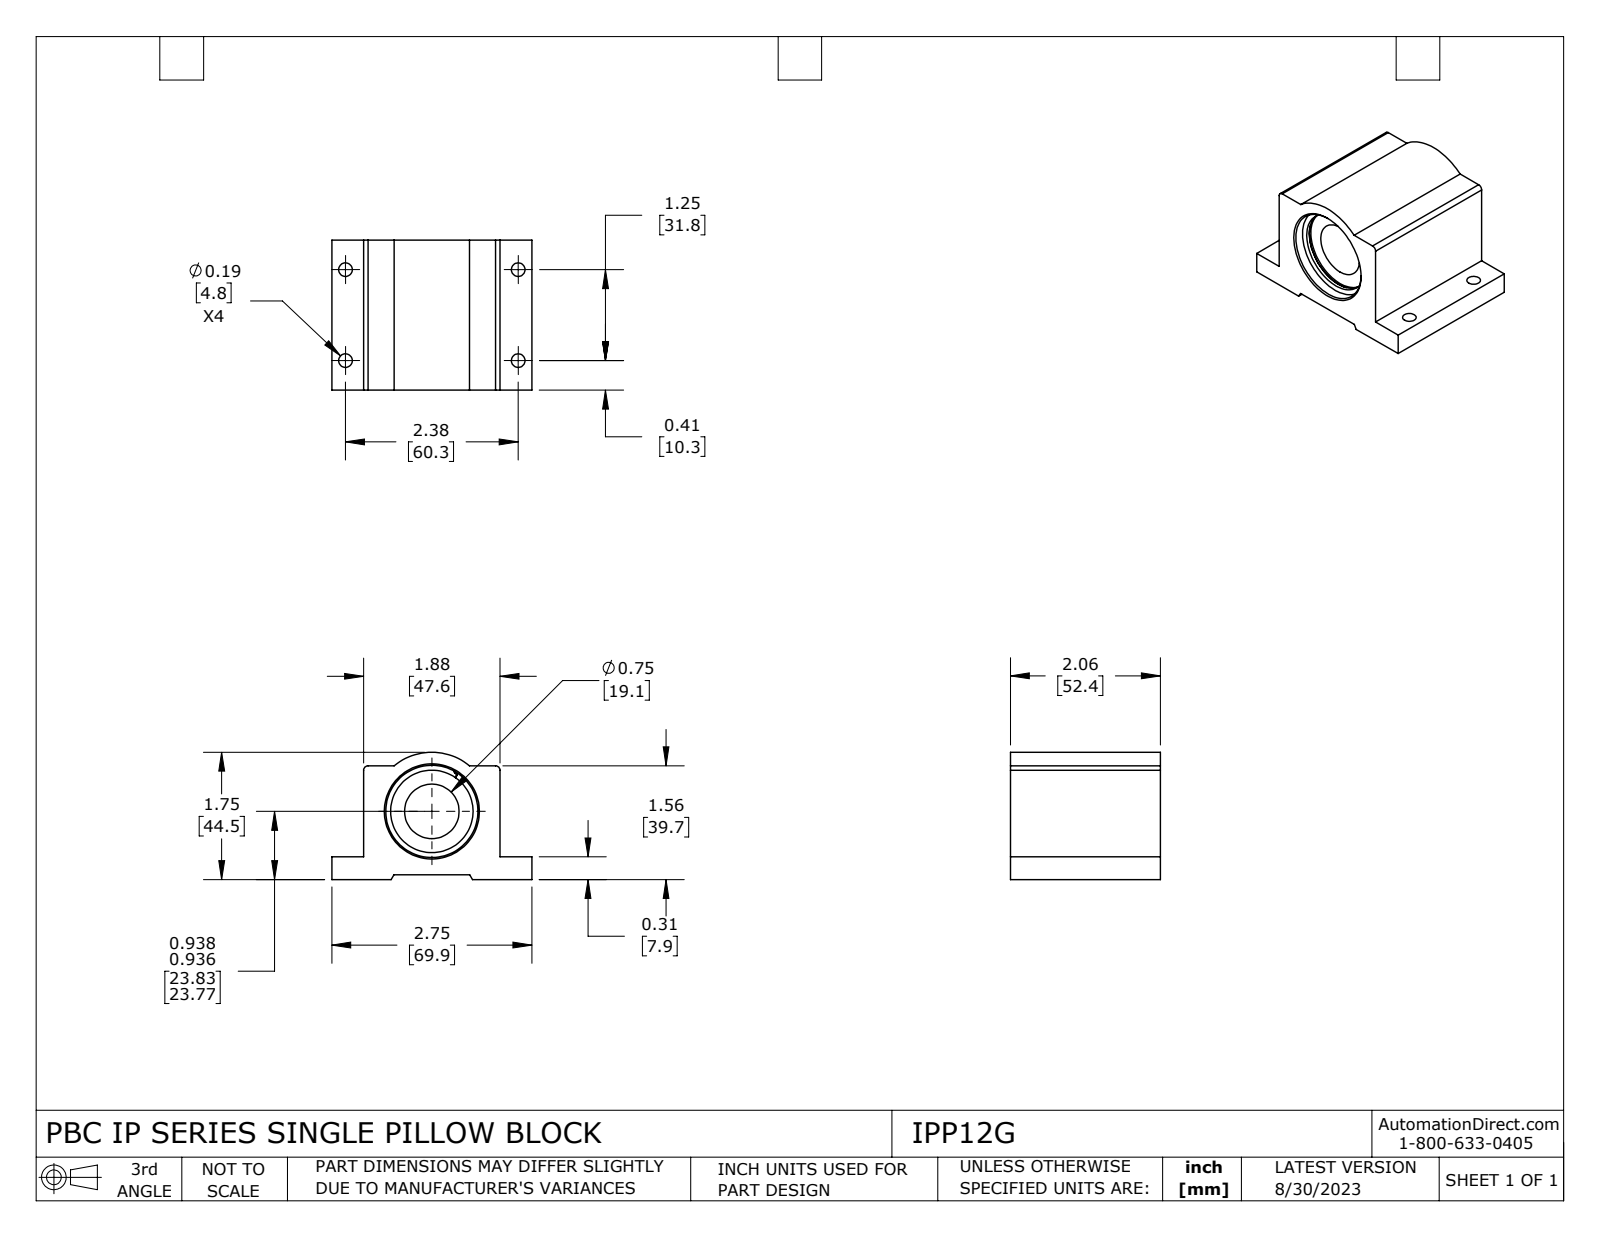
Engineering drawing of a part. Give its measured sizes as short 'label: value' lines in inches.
name: IPP12G
written by: SolidWorks 2021 (CONFIG_CONTROL_DESIGN)
unit: in
bodies: 4 solids, 126 faces (43 planar, 63 cylindrical, 20 other)
size: 2.75 × 2.063 × 1.75
volume: 5.358 in³; area: 45.8 in²
holes: 4× ⌀0.187, 1× ⌀0.75, 1× ⌀1.133, 1× ⌀1.138, 1× ⌀1.267, 1× ⌀1.33
bosses: 1× ⌀1.339, 1× ⌀1.25, 1× ⌀1.176
rounds: 4× R0.017, 2× R0.012, 2× R0.022, 2× R0.06, 1× R0.813
face distances: 1.875, 0.065, 2.062, 0.312, 0.247, 1.563, 1.498, 1.251, 0.437, 2.312
hole spacings: 1.25, 2.375, 2.684
